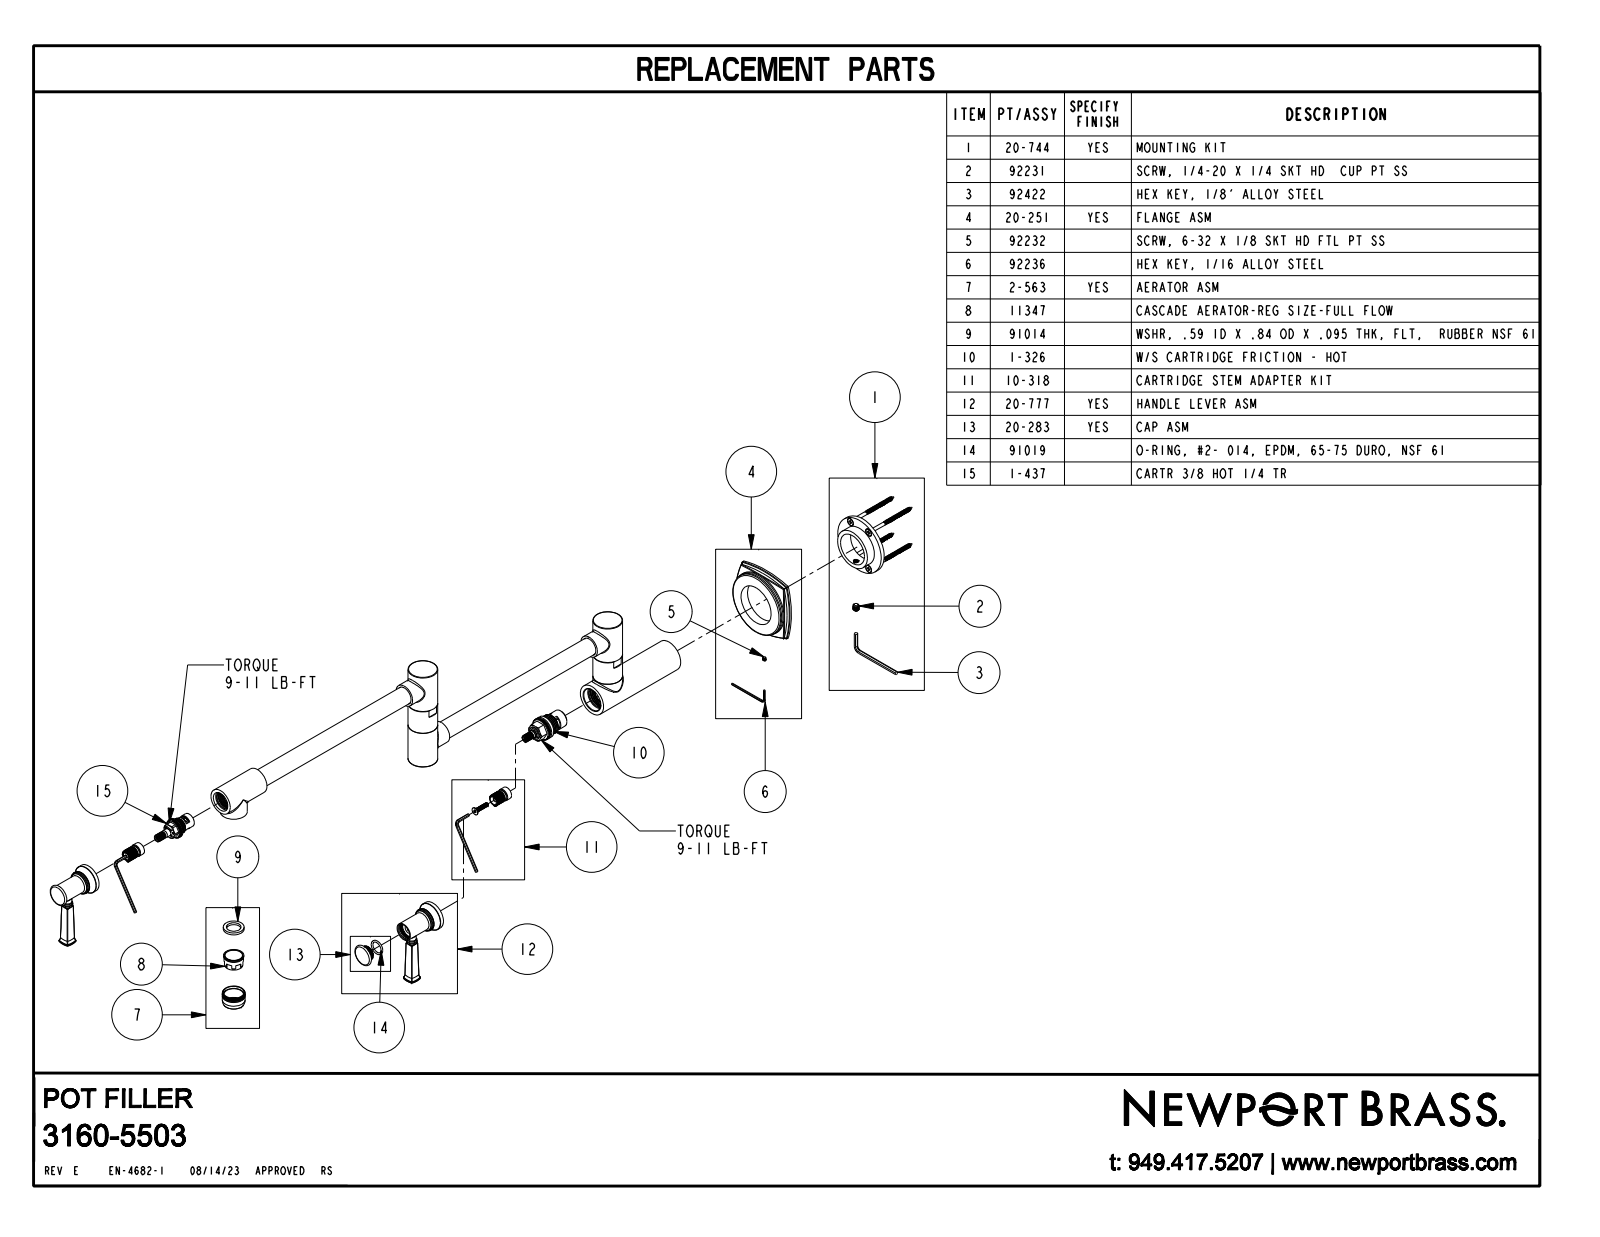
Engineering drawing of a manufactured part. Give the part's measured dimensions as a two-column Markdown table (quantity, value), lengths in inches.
| quantity | value |
| --- | --- |
| part name | 3160-5503 |
| STEP written by | CREO PARAMETRIC BY PTC INC, 2018400 (CONFIG_CONTROL_DESIGN) |
| units | inches |
| bodies | 1 solid, 415 faces (35 planar, 76 cylindrical, 304 other) |
| overall size | 27.444 × 8.946 × 2.9 |
| volume | 31.32 in³ |
| surface area | 140.1 in² |
| round bosses / shafts (diameter × count) | 0.94 × 4, 1.2 × 2, 1.19 × 2, 1.1 × 2, 0.76 × 2, 0.75 × 2, 0.35 × 2, 1.325 × 1 |
| partial cylindrical surfaces (radius × count) | 0.02 × 8, 0.03 × 8, 0.8 × 8, 4.62 × 4, 4.684 × 4, 0.472 × 1 |
| main face-to-face distances | 0.57, 2.86, 1.576, 4.437, 21.248, 1.775, 1.676, 0.02, 1.696, 4.41 |
